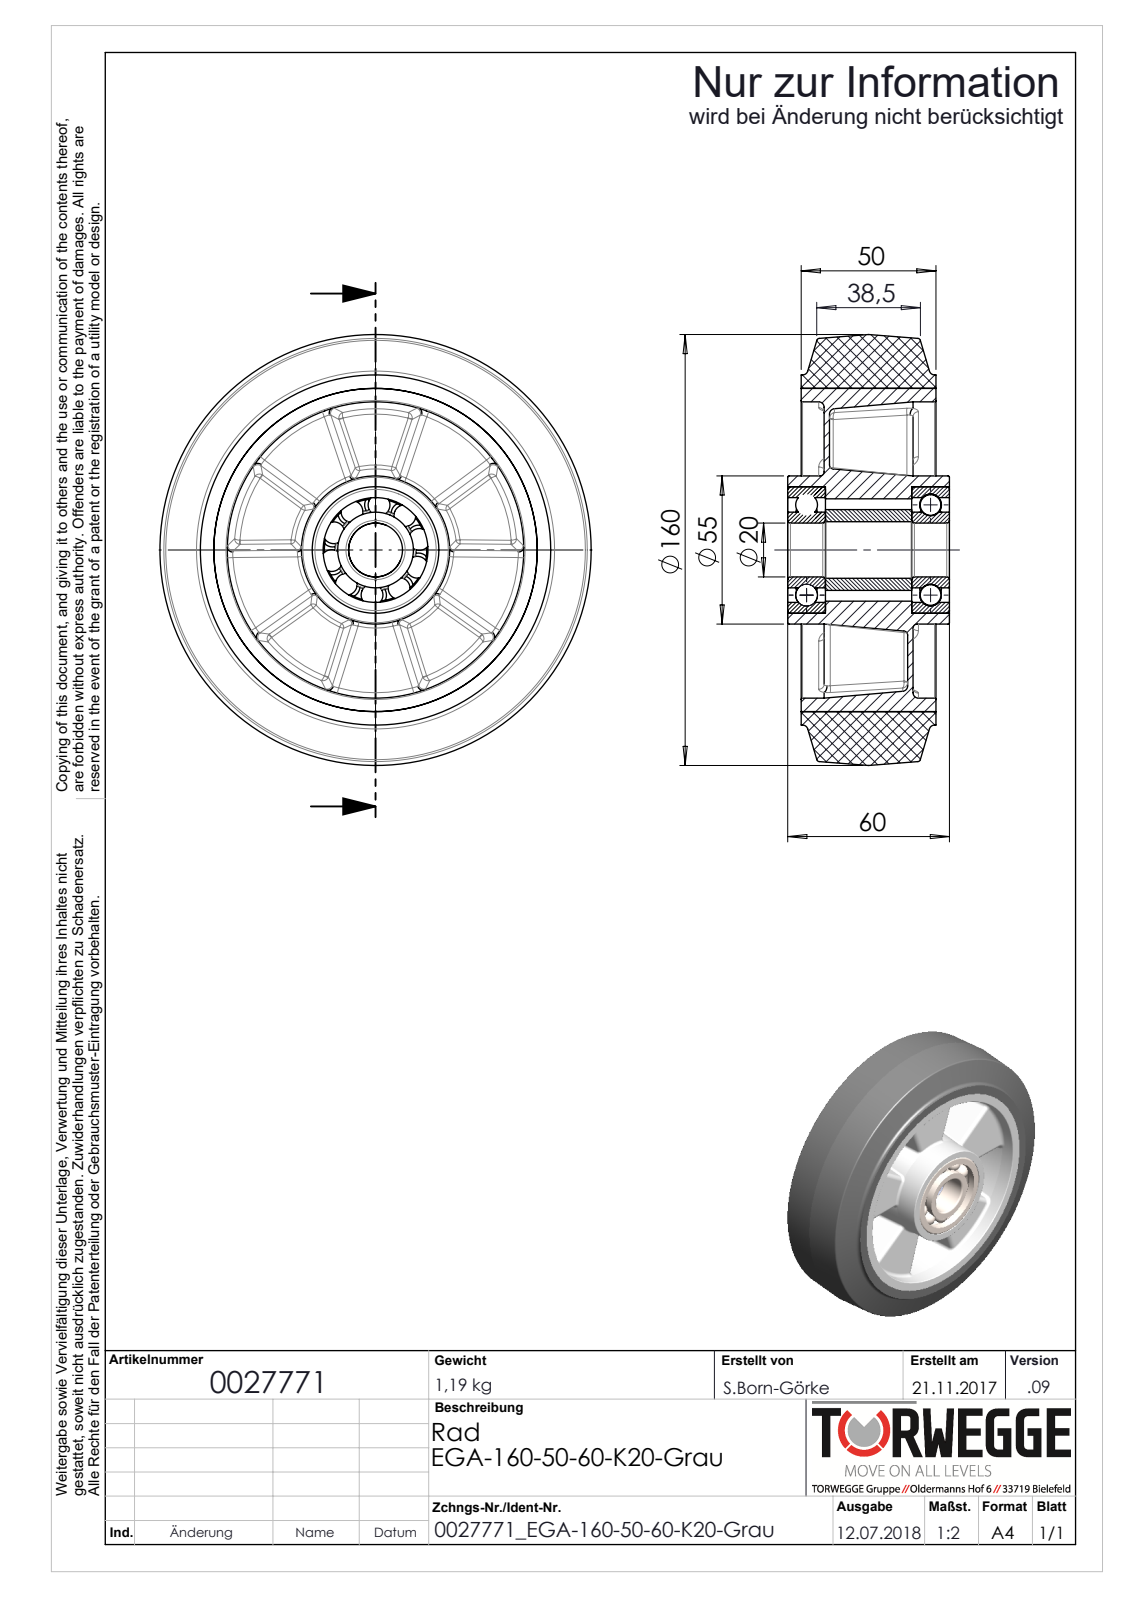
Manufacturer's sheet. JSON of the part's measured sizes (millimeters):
{"part_name": "0027771_EGA-160-50-60-K20-grau", "step_written_by": "SolidWorks 2014 (AUTOMOTIVE_DESIGN)", "units": "millimeters", "bodies": {"solids": 5, "faces": 463, "planar": 62, "cylindrical": 98, "other": 303}, "overall_size": [160, 160, 60], "volume_mm3": 617320, "surface_area_mm2": 160547, "round_holes": [[20, 1], [21, 1], [38, 1], [38.9, 1], [47, 1], [110, 1], [120, 1]], "round_bosses_or_shafts": [[130, 1], [55, 1], [30, 1], [28.1, 1]], "partial_cylinders_radius": [[1.5, 20], [2.5, 20]], "face_to_face_distances": [8.5, 41.5, 0.5, 1.5, 50, 13.5, 46, 14, 44.5, 2.87]}
